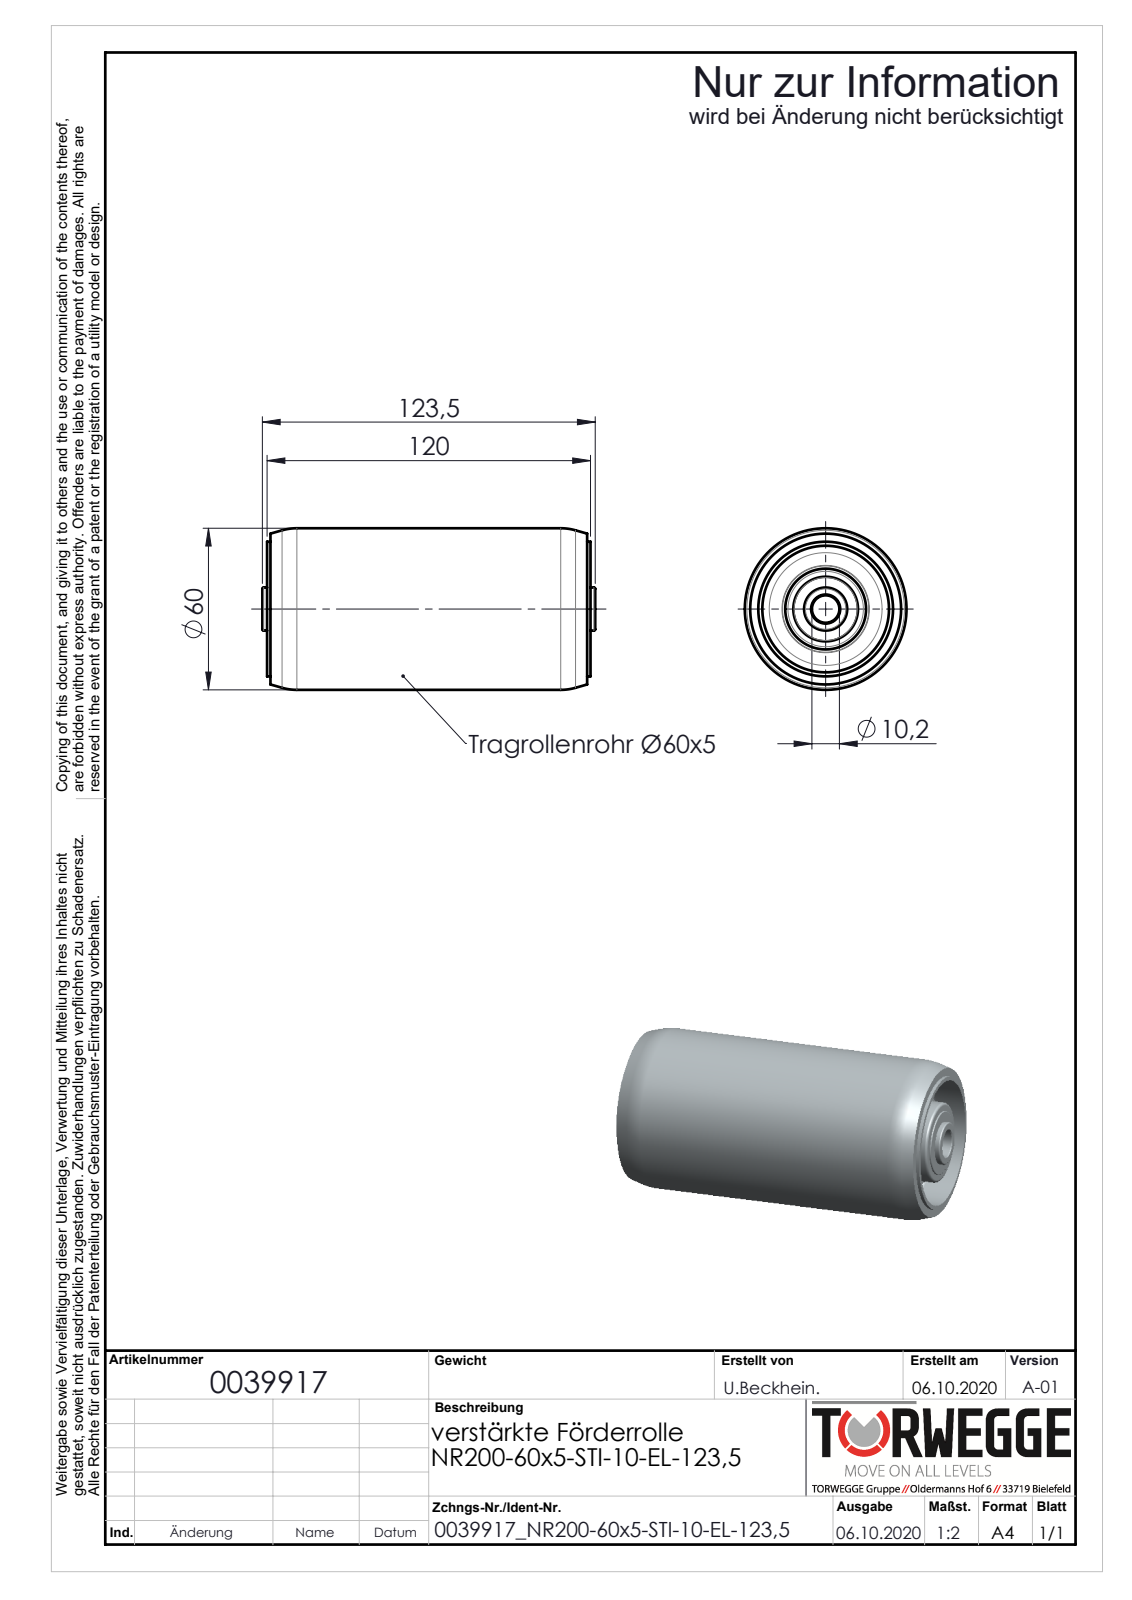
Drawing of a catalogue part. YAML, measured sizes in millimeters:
part_name: "0039917"
step_written_by: "SolidWorks 2018 (AUTOMOTIVE_DESIGN)"
units: millimeters
bodies: {solids: 1, faces: 72, planar: 12, cylindrical: 24, other: 36}
overall_size: [123.5, 60, 60]
volume: 303176
surface_area: 36616
round_holes:
  - {diameter: 10.2, count: 1}
  - {diameter: 47, count: 1}
round_bosses_or_shafts:
  - {diameter: 60, count: 1}
  - {diameter: 50, count: 1}
  - {diameter: 30, count: 1}
  - {diameter: 24, count: 1}
  - {diameter: 16, count: 1}
face_to_face_distances: [0.5, 118.5, 117.5, 1, 1.25, 118.75, 119.75, 0.75, 119.25, 119]
